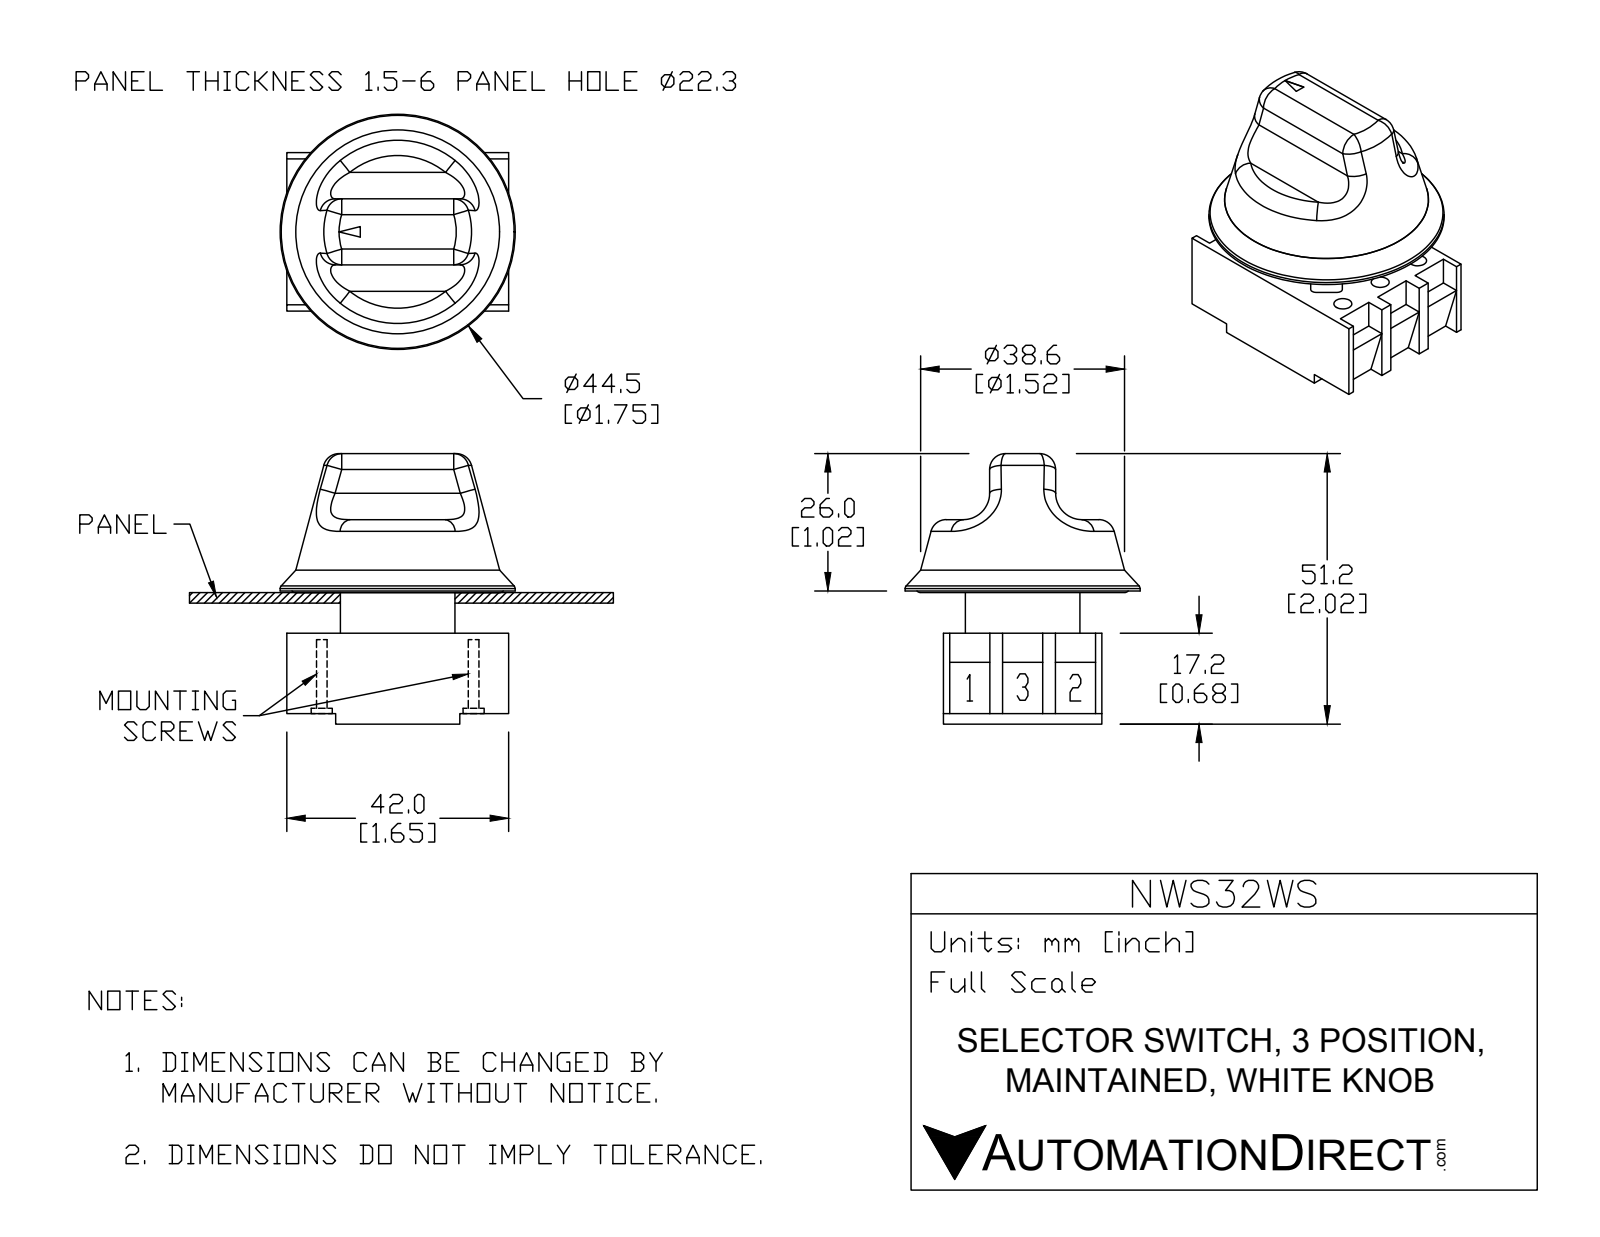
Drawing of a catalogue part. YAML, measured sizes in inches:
part_name: "NWS32WS"
step_written_by: "SolidWorks 2015 (AUTOMOTIVE_DESIGN)"
units: inches
bodies: {solids: 7, faces: 236, planar: 134, cylindrical: 67, other: 35}
overall_size: [2.016, 1.752, 1.752]
volume: 2.137
surface_area: 29.6
round_holes:
  - {diameter: 0.134, count: 6}
  - {diameter: 0.197, count: 6}
  - {diameter: 0.492, count: 1}
round_bosses_or_shafts:
  - {diameter: 0.181, count: 2}
  - {diameter: 0.157, count: 2}
  - {diameter: 1.752, count: 1}
  - {diameter: 0.854, count: 1}
partial_cylinders:
  - {radius: 0.039, count: 8}
  - {radius: 0.343, count: 5}
  - {radius: 0.118, count: 2}
  - {radius: 0.197, count: 2}
  - {radius: 0.433, count: 1}
face_to_face_distances: [0.156, 1.181, 0.315, 0.47, 0.303, 0.167, 0.394, 0.598, 0.902, 0.913]
hole_center_spacings: [0.394, 0.69, 1.199, 1.132, 0.566, 0.787, 1.379]
